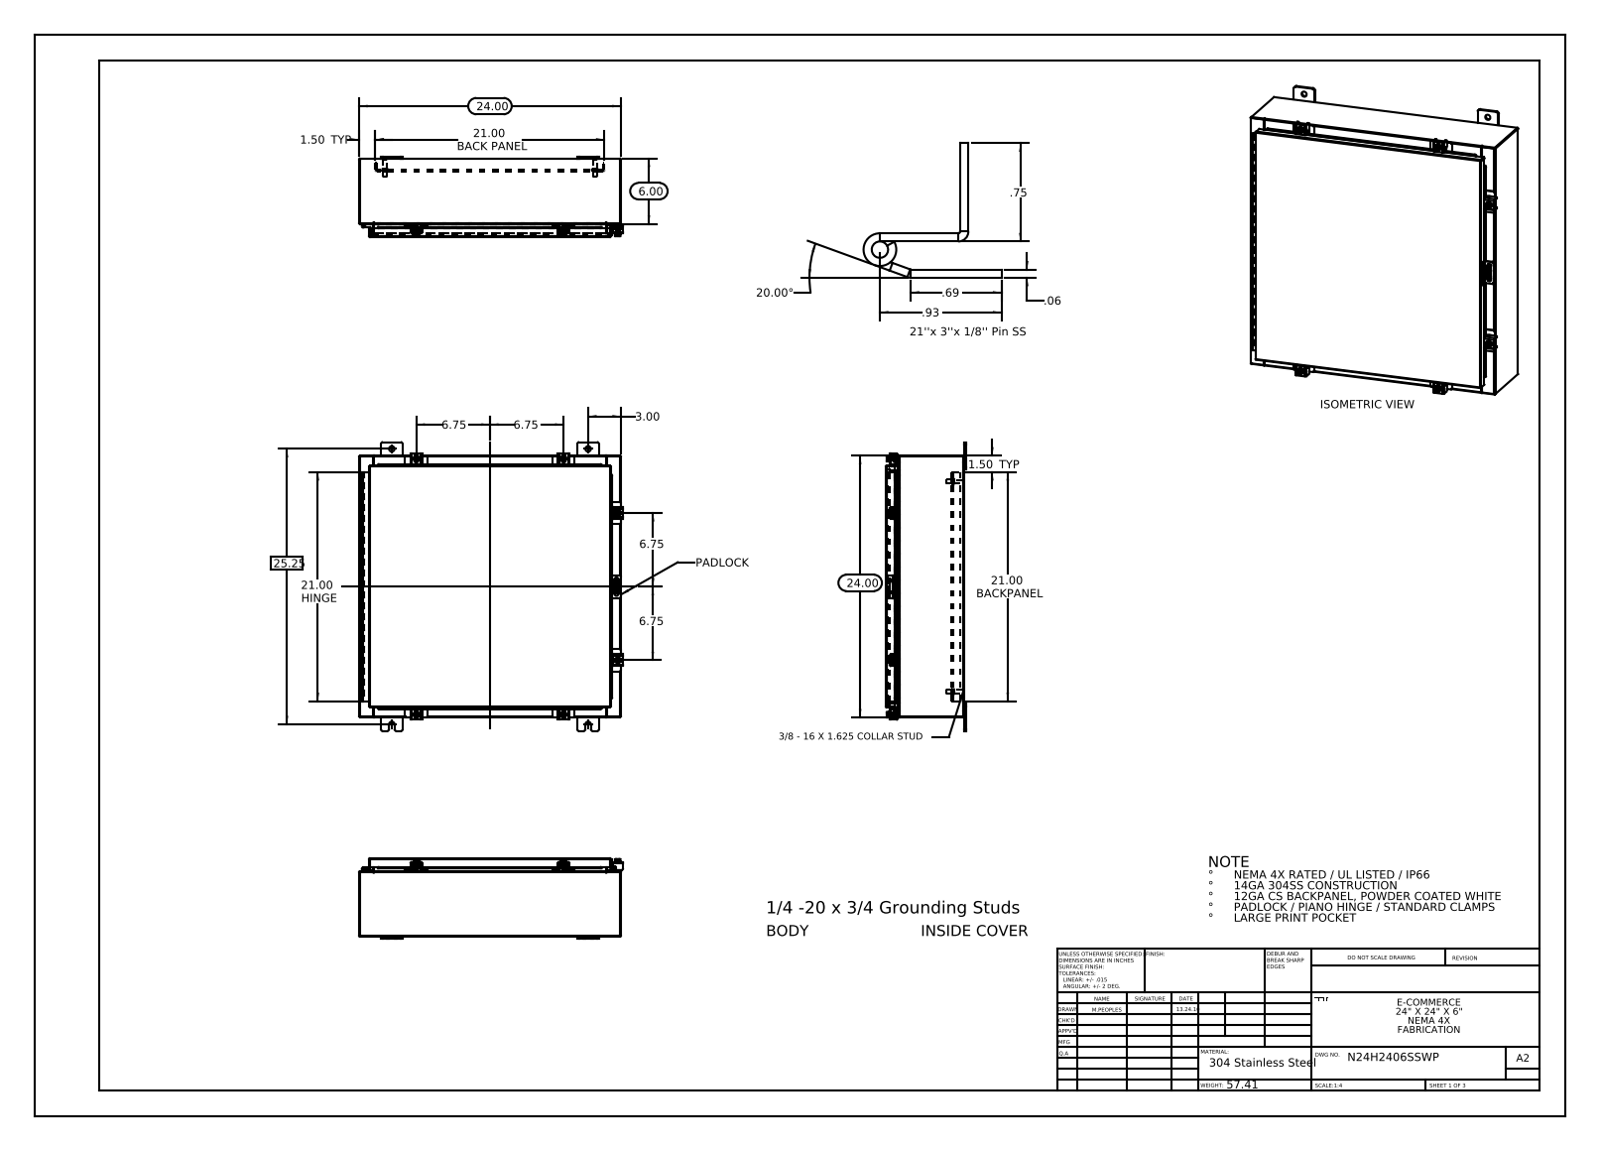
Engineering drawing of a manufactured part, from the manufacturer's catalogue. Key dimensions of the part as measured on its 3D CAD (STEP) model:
Part name (STEP PRODUCT): N24H2406SSWP Standard Clamps; N24H2406SSWP Padlock Hasp; N24H2406SSWP Top; N24H2406SSWP Padlock Staple (+8 more)
STEP written by: SolidWorks 2013 (CONFIG_CONTROL_DESIGN)
Units: inches
Bodies: 47 solids, 1709 faces (908 planar, 705 cylindrical, 96 other)
Overall size (bounding box): 26.5 × 24.211 × 7.389
Volume: 201.9 in³ · Surface area: 5 048 in²
Round holes (diameter × count): ⌀0.5 ×8, ⌀0.213 ×6, ⌀0.26 ×6, ⌀0.125 ×2, ⌀0.125 ×1
Round bosses / shafts (diameter × count): ⌀0.25 ×7, ⌀0.5 ×6, ⌀0.399 ×6, ⌀0.625 ×4, ⌀0.375 ×4, ⌀0.33 ×4
Partial cylindrical surfaces — rounded edges, fillets, slot ends (radius × count): R0.06 ×30, R0.013 ×25, R0.19 ×24, R0.088 ×21, R0.12 ×12, R0.141 ×12, R0.125 ×10, R0.05 ×9
Main face-to-face distances: 0.075, 7.126, 23.925, 7.201, 7.051, 0.104, 1, 1.075, 6.051, 6.126
Hole centre spacings: 16.509, 19.134, 21.544, 26.907, 13.5, 1.858, 2.277, 2.423
